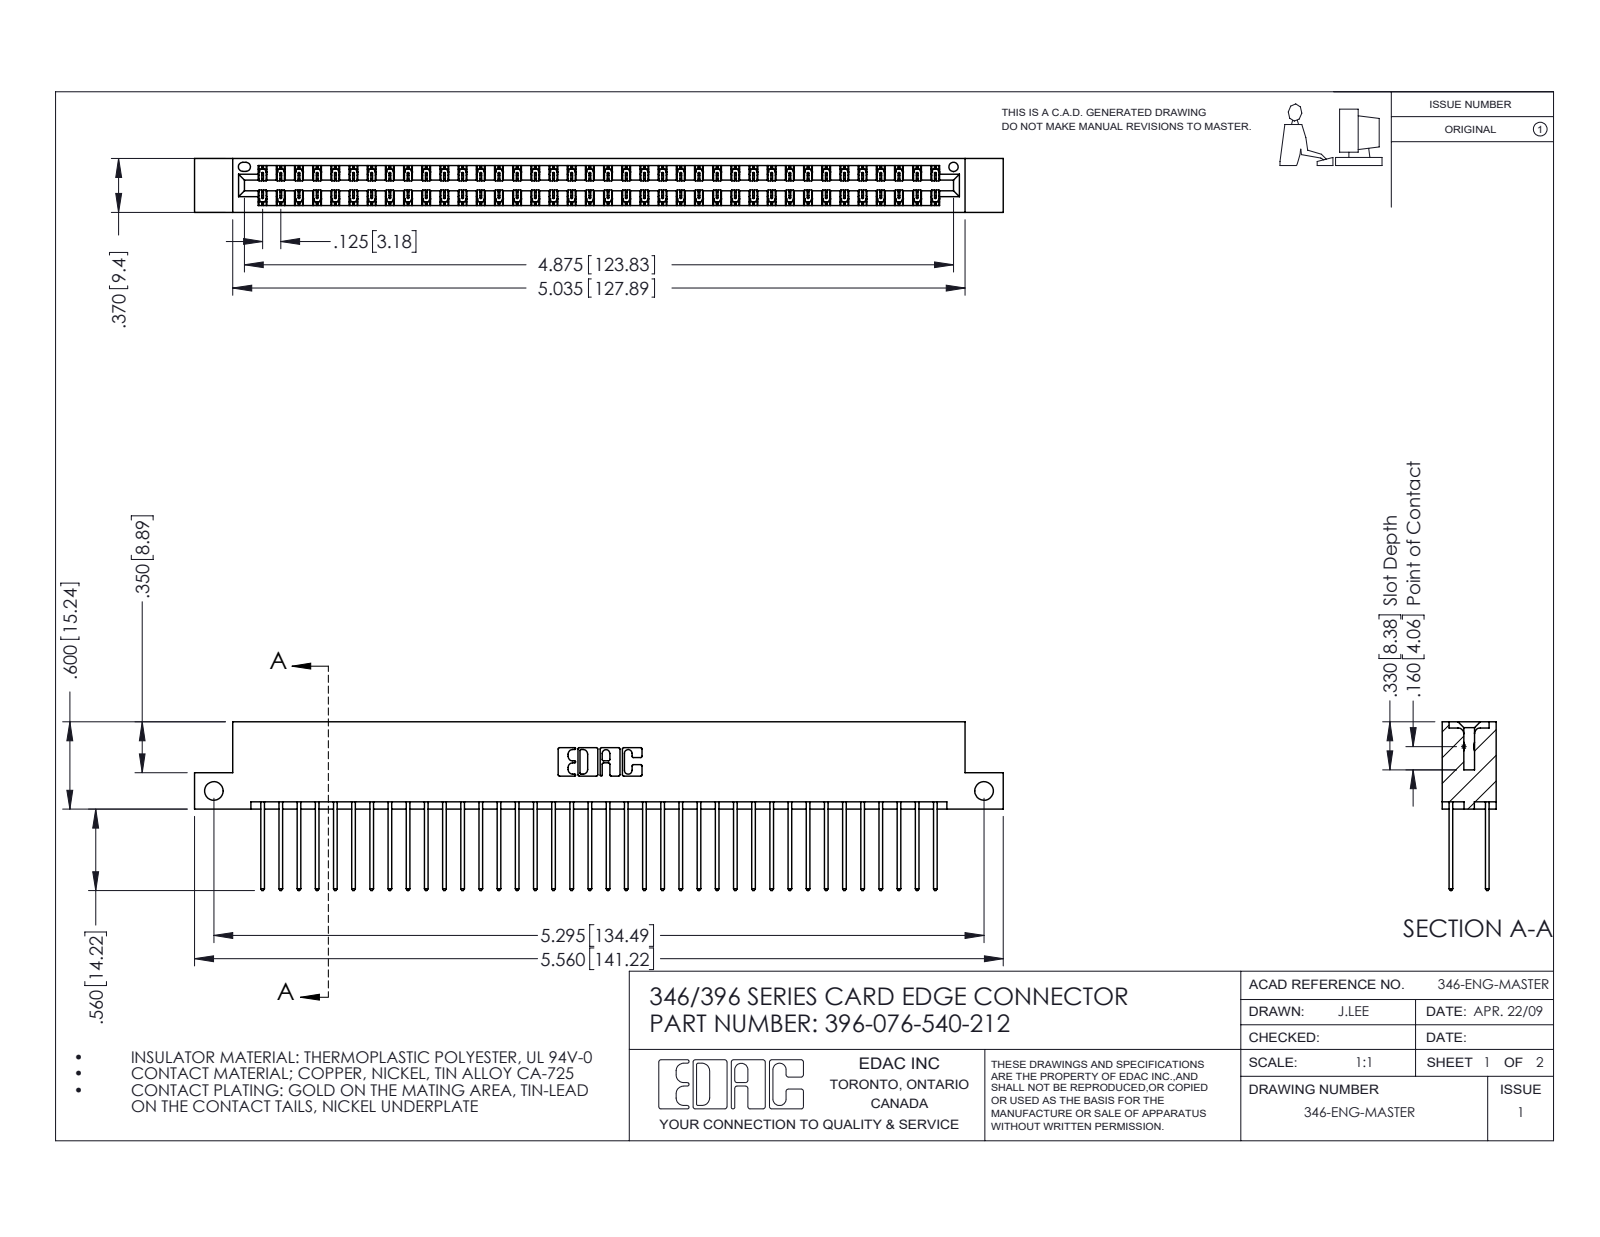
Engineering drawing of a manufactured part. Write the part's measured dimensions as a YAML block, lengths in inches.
part_name: "345-292-001_345-293-140; 396-076-540-212; 346 Part_Flush Mounting Lugs - Side Mount"
step_written_by: "SolidWorks 2016 (CONFIG_CONTROL_DESIGN)"
units: inches
bodies: {solids: 77, faces: 4074, planar: 2736, cylindrical: 1338, other: 0}
overall_size: [5.56, 1.16, 0.37]
volume: 0.851
surface_area: 31.5
round_holes:
  - {diameter: 0.128, count: 2}
  - {diameter: 0.064, count: 1}
partial_cylinders:
  - {radius: 0.006, count: 114}
  - {radius: 0.01, count: 76}
  - {radius: 0.01, count: 22}
  - {radius: 0.007, count: 6}
  - {radius: 0.031, count: 6}
  - {radius: 0.026, count: 3}
  - {radius: 0.014, count: 2}
  - {radius: 0.022, count: 2}
face_to_face_distances: [0.048, 0.322, 0.25, 0.072, 0.298, 0.025, 0.37, 0.275, 0.148, 0.222]
hole_center_spacings: [5.295]
